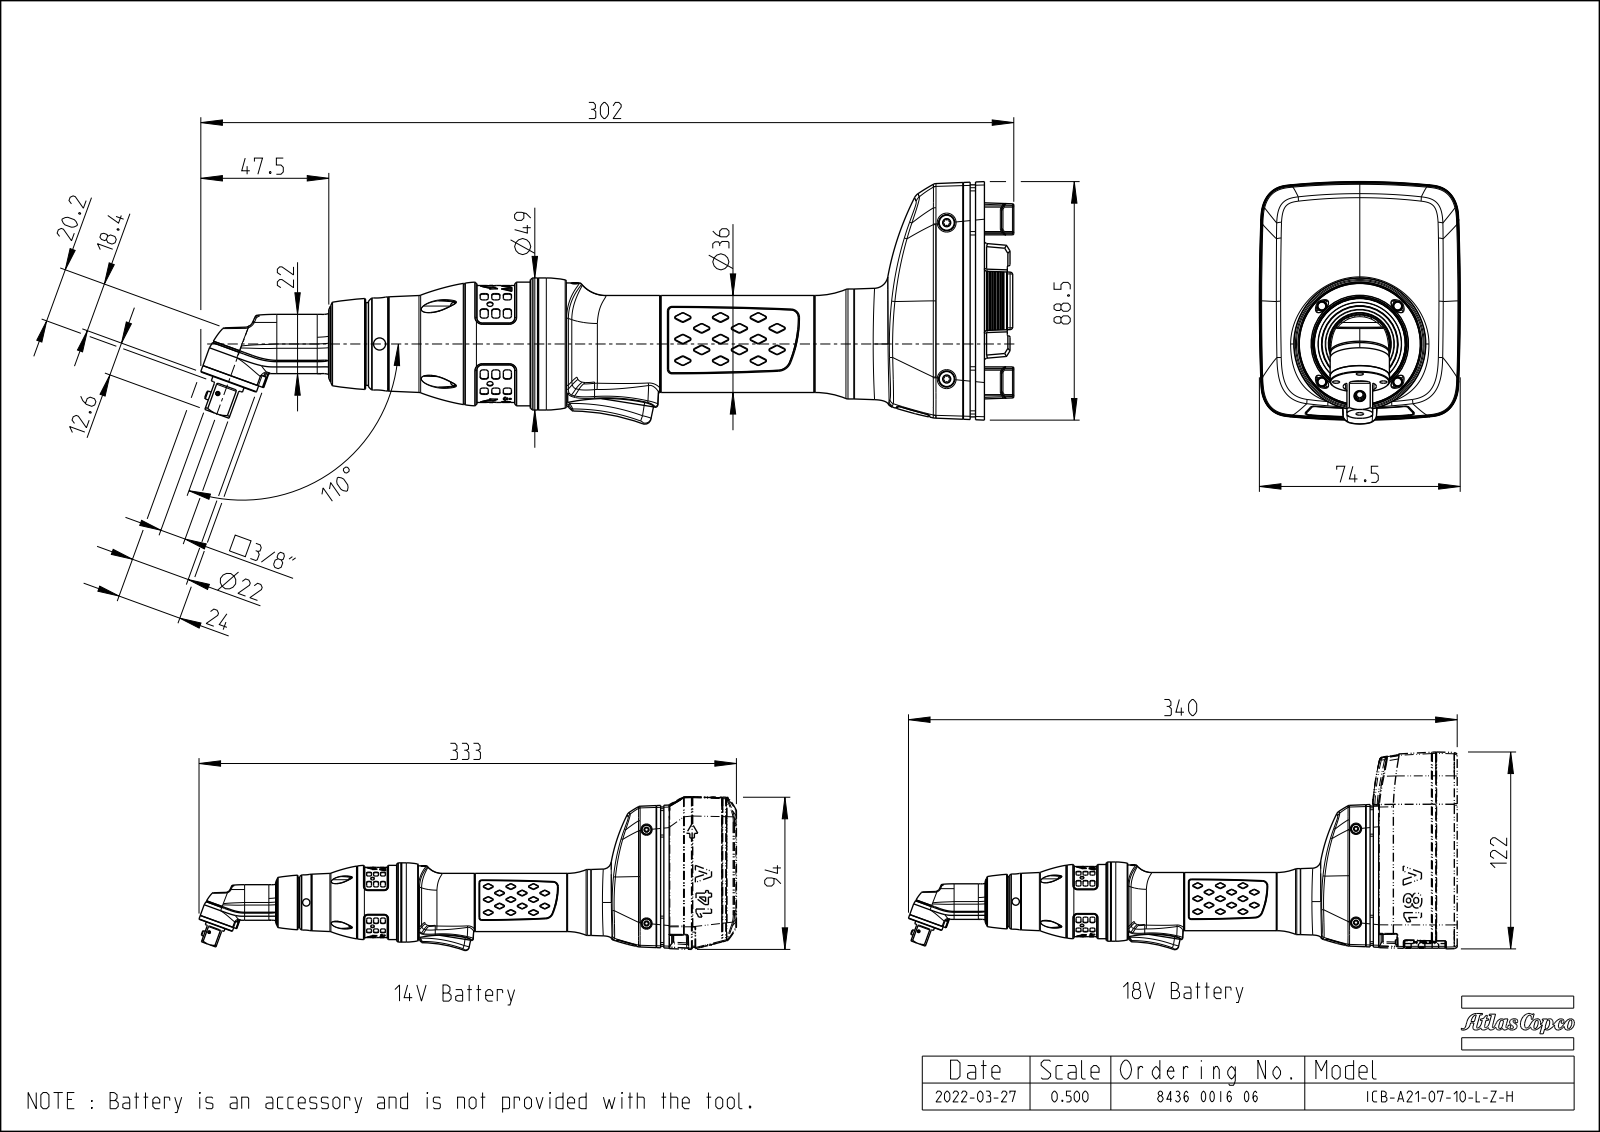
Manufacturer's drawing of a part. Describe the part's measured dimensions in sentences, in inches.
The part is named "EXT_COMP_SW0016". Its 3-D file was written by "CREO PARAMETRIC BY PTC INC, 2020281 (CONFIG_CONTROL_DESIGN)". It is 2 solids with 2599 faces: 759 planar, 641 cylindrical and 1199 other. Overall it measures 11.882 by 3.543 by 2.935 inches. Its volume is 28.84 cubic inches and its surface area 102.7 square inches. Round holes: 4 of diameter 0.102, 2 of diameter 0.177, 2 of diameter 0.236, 1 of diameter 0.028, 1 of diameter 0.047, 1 of diameter 0.059, 1 of diameter 0.138, 1 of diameter 1.787. Round bosses or shafts: 4 of diameter 0.315, 4 of diameter 0.125, 4 of diameter 0.115, 3 of diameter 0.22, 1 of diameter 1.929, 1 of diameter 1.866, 1 of diameter 1.807, 1 of diameter 1.783. Partial cylindrical surfaces (rounded edges, fillets, slot ends): 92 of radius 0.02, 54 of radius 0.039, 30 of radius 0.011, 30 of radius 0.02, 24 of radius 0.015, 24 of radius 0.027, 14 of radius 0.012, 12 of radius 0.079. The main face-to-face distances are 4.744, 4.743, 0.118, 0.413, 0.331, 5.156, 5.157, 2.362, 0.425, 4.731. The hole center spacings are 0.346, 0.49, 0.693, 2.283, 2.473, 8.305, 8.477, 9.077.
